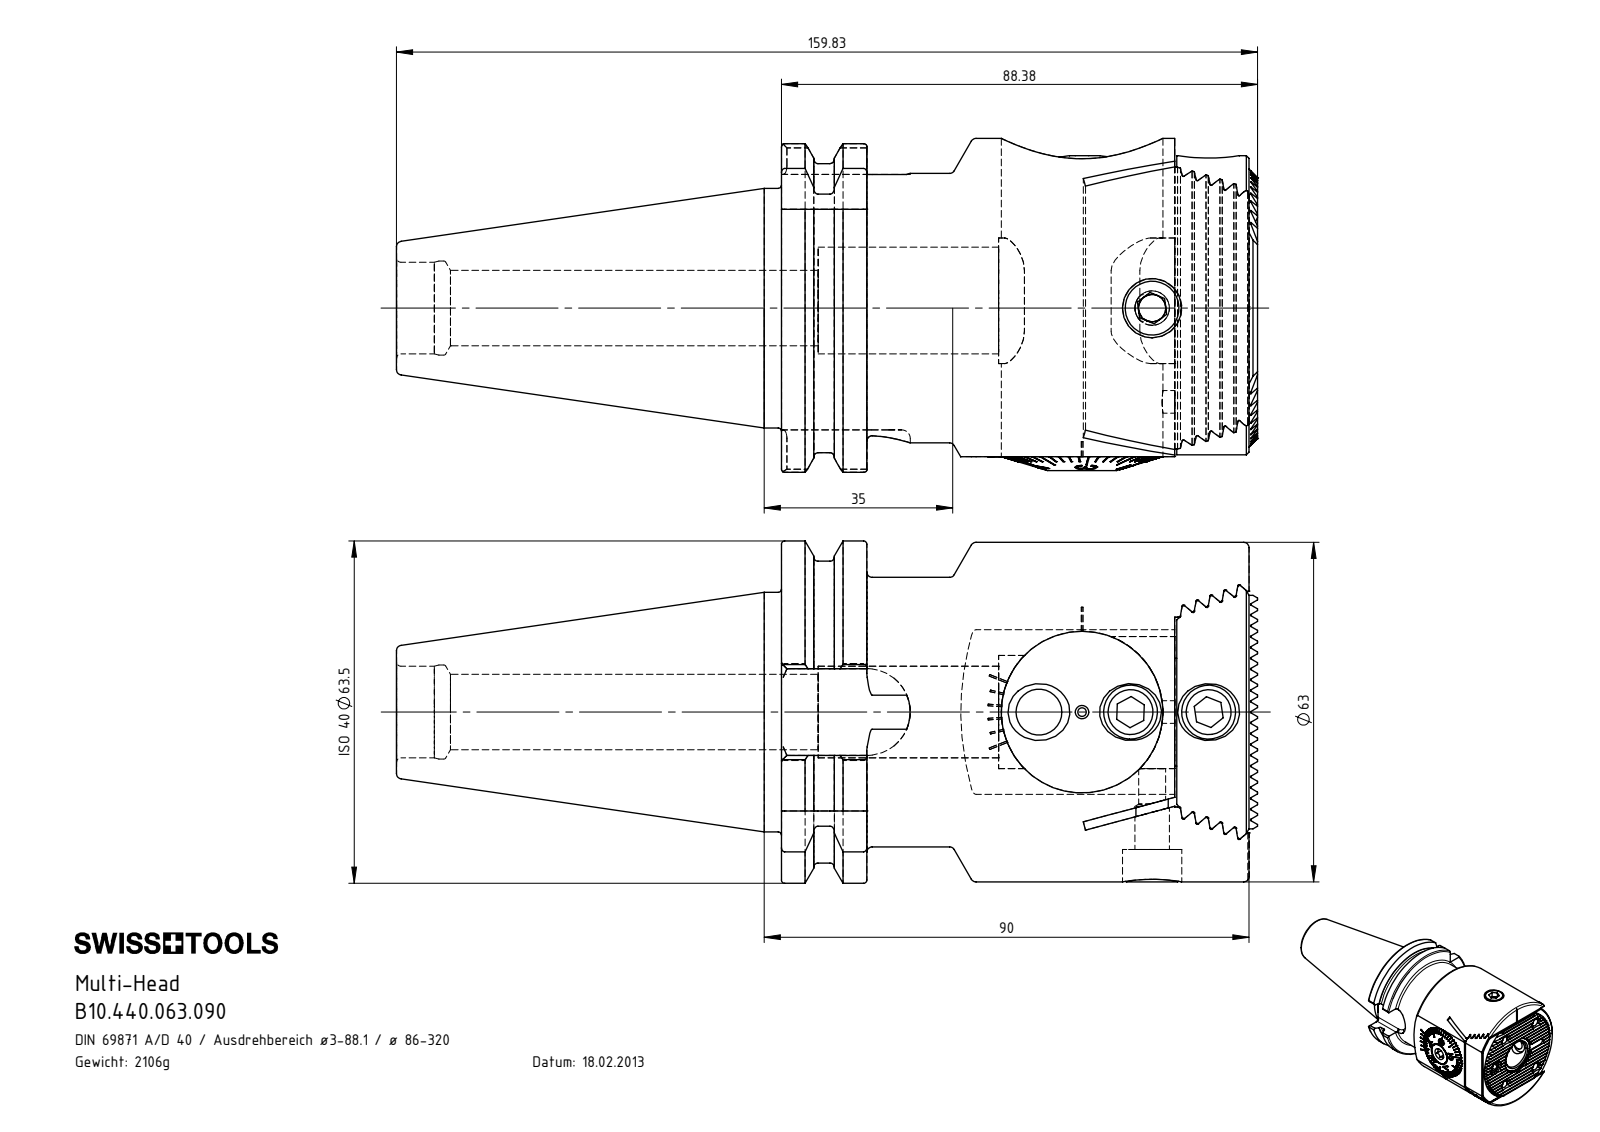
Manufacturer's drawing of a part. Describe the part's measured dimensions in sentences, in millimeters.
The part is named "ISO 4026 - M8 x 6; A55-BG2.012.006_B; ISO 4762 - M6 x 16; SK4-MH1.K00.090_A (+8 more)". Its 3-D file was written by "SolidWorks 2017 (CONFIG_CONTROL_DESIGN)". It is 14 solids with 1118 faces: 556 planar, 253 cylindrical and 309 other. Overall it measures 159.83 by 63.5 by 61.95 millimeters. Its volume is 268 319 cubic millimeters and its surface area 74 290 square millimeters. Round holes: 5 of diameter 4.2, 4 of diameter 8.5, 3 of diameter 6.8, 3 of diameter 11, 2 of diameter 14, 2 of diameter 20, 1 of diameter 1, 1 of diameter 1.6, 1 of diameter 3.3, 1 of diameter 5, 1 of diameter 6.4, 1 of diameter 8. Round bosses or shafts: 3 of diameter 10, 1 of diameter 63, 1 of diameter 50, 1 of diameter 44.45, 1 of diameter 30, 1 of diameter 29.98, 1 of diameter 29.9, 1 of diameter 25. Partial cylindrical surfaces (rounded edges, fillets, slot ends): 21 of radius 0.14, 20 of radius 0.2, 8 of radius 1.6, 6 of radius 6, 2 of radius 4, 2 of radius 31, 1 of radius 2, 1 of radius 7. The main face-to-face distances are 2.38, 0.4, 1.73, 73, 73.4, 7.15, 4.77, 4.76, 8.66, 5.2. The hole center spacings are 16.73, 18.03, 20.52, 24, 30, 34.8, 38.42, 7.28.
